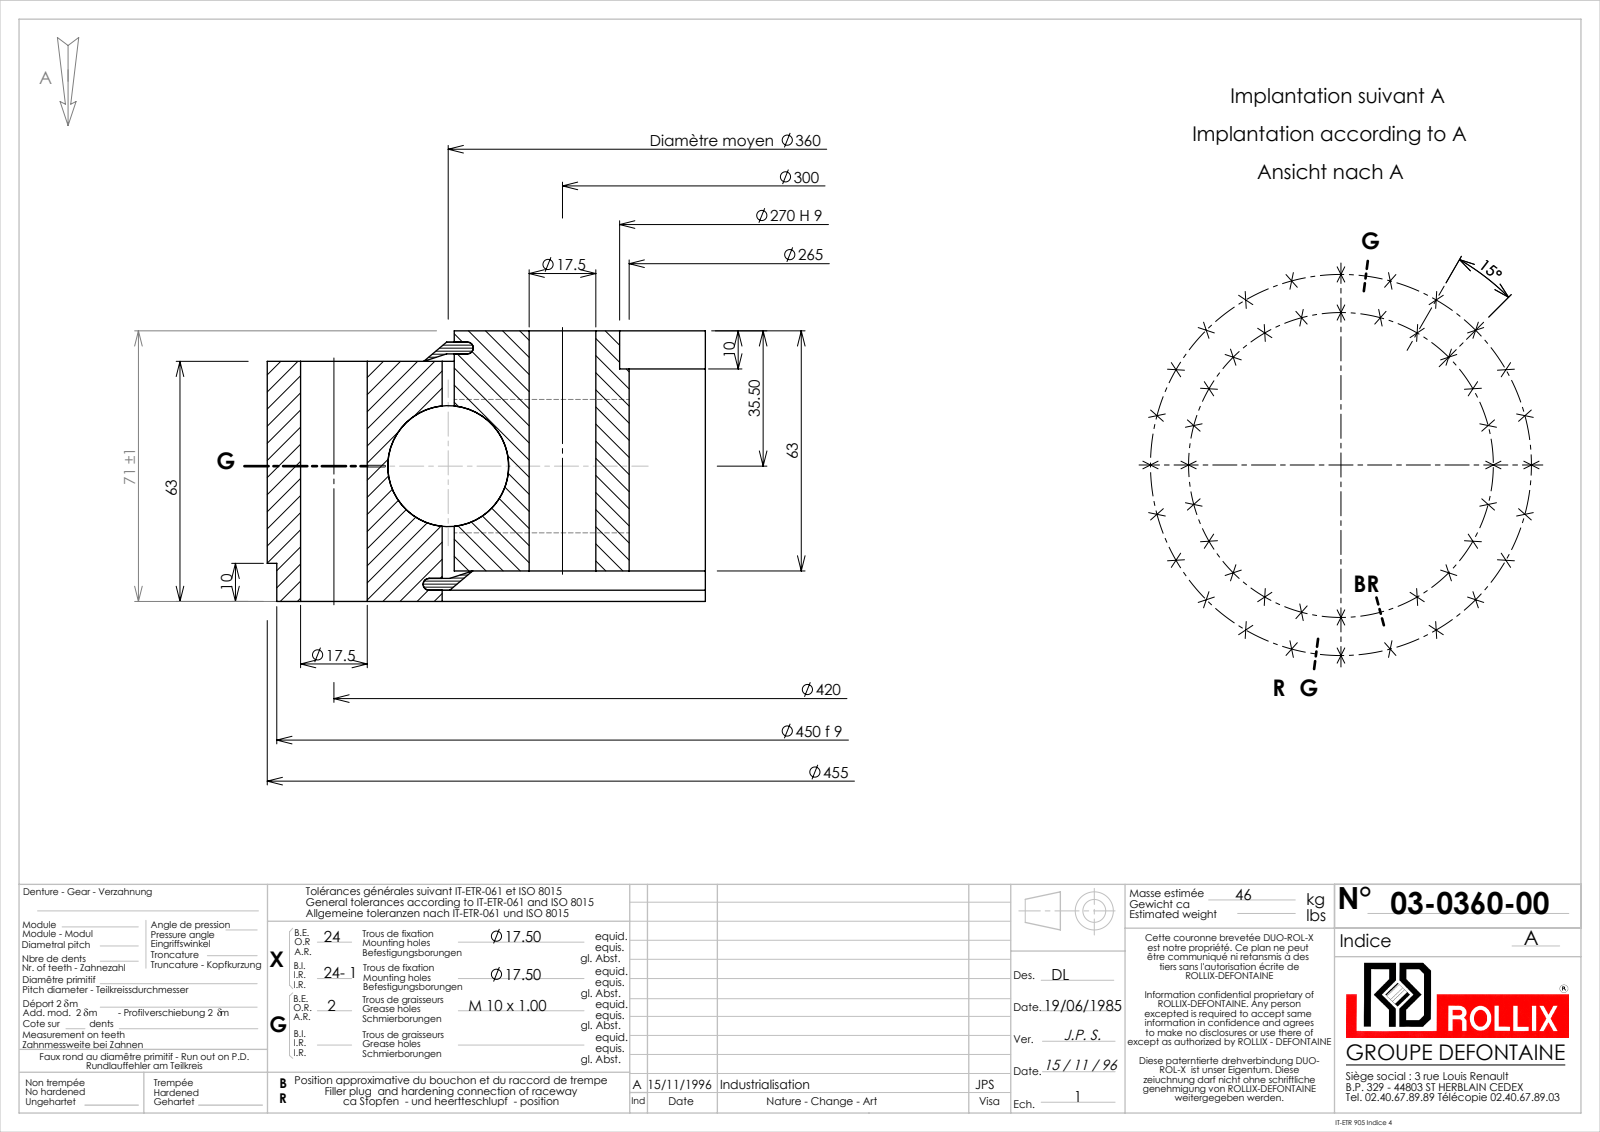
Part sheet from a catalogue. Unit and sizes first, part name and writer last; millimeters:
Units: millimetres
Overall size (bounding box): 455 × 455 × 71
Round holes (diameter × count): ⌀17.5 ×47, ⌀9 ×2, ⌀265 ×1, ⌀270 ×1, ⌀363.18 ×1
Round bosses / shafts (diameter × count): ⌀455 ×1, ⌀450 ×1, ⌀356.83 ×1
Main face-to-face distances: 63, 8, 55, 71, 6.05, 64.95, 1.95, 56.95, 2.95, 68.05
Hole centre spacings: 150, 212.13, 259.81, 39.16, 77.65, 182.63, 238.01, 114.8
Volume: 5 040 000 mm³ · Surface area: 759 054 mm²
Bodies: 5 solids, 160 faces (14 planar, 118 cylindrical, 28 other)
Part name (STEP PRODUCT): 03-0360-00
STEP written by: SolidWorks 2016 (CONFIG_CONTROL_DESIGN)
